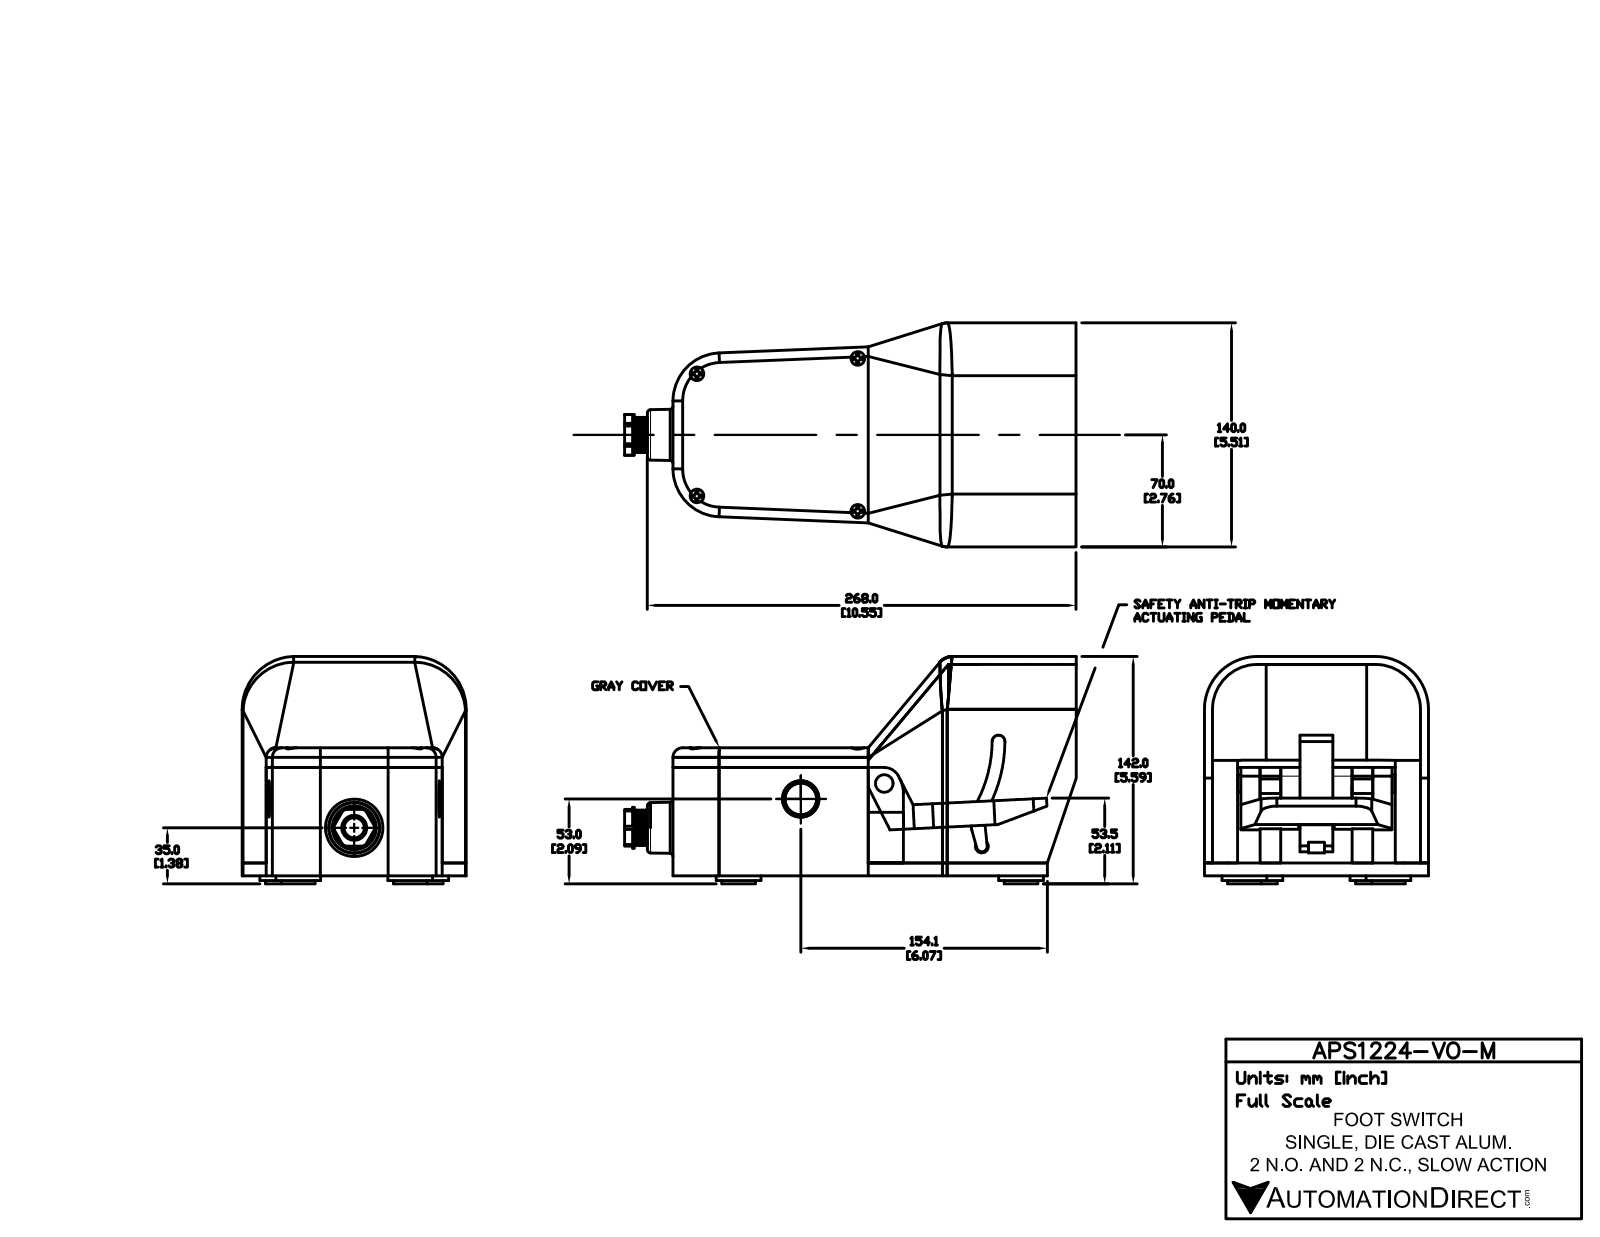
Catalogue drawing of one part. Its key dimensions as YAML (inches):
part_name: "APS1224-V0-M"
step_written_by: "SolidWorks 2015 (AUTOMOTIVE_DESIGN)"
units: inches
bodies: {solids: 19, faces: 379, planar: 220, cylindrical: 103, other: 56}
overall_size: [11.112, 5.591, 5.512]
volume: 94.77
surface_area: 422.3
round_holes:
  - {diameter: 0.335, count: 4}
  - {diameter: 0.896, count: 2}
  - {diameter: 0.498, count: 1}
  - {diameter: 0.614, count: 1}
round_bosses_or_shafts:
  - {diameter: 1.102, count: 4}
  - {diameter: 0.827, count: 4}
  - {diameter: 0.782, count: 2}
  - {diameter: 1.004, count: 1}
  - {diameter: 0.866, count: 1}
  - {diameter: 0.433, count: 1}
partial_cylinders:
  - {radius: 0.039, count: 16}
  - {radius: 0.394, count: 7}
  - {radius: 0.236, count: 3}
  - {radius: 0.787, count: 2}
  - {radius: 1.102, count: 2}
  - {radius: 1.181, count: 2}
  - {radius: 1.299, count: 2}
  - {radius: 0.132, count: 1}
face_to_face_distances: [0.197, 5.315, 0.315, 2.348, 2.664, 2.349, 2.663, 5.512, 3.15, 2.835]
hole_center_spacings: [3.976, 5.206, 3.004, 3.76]
